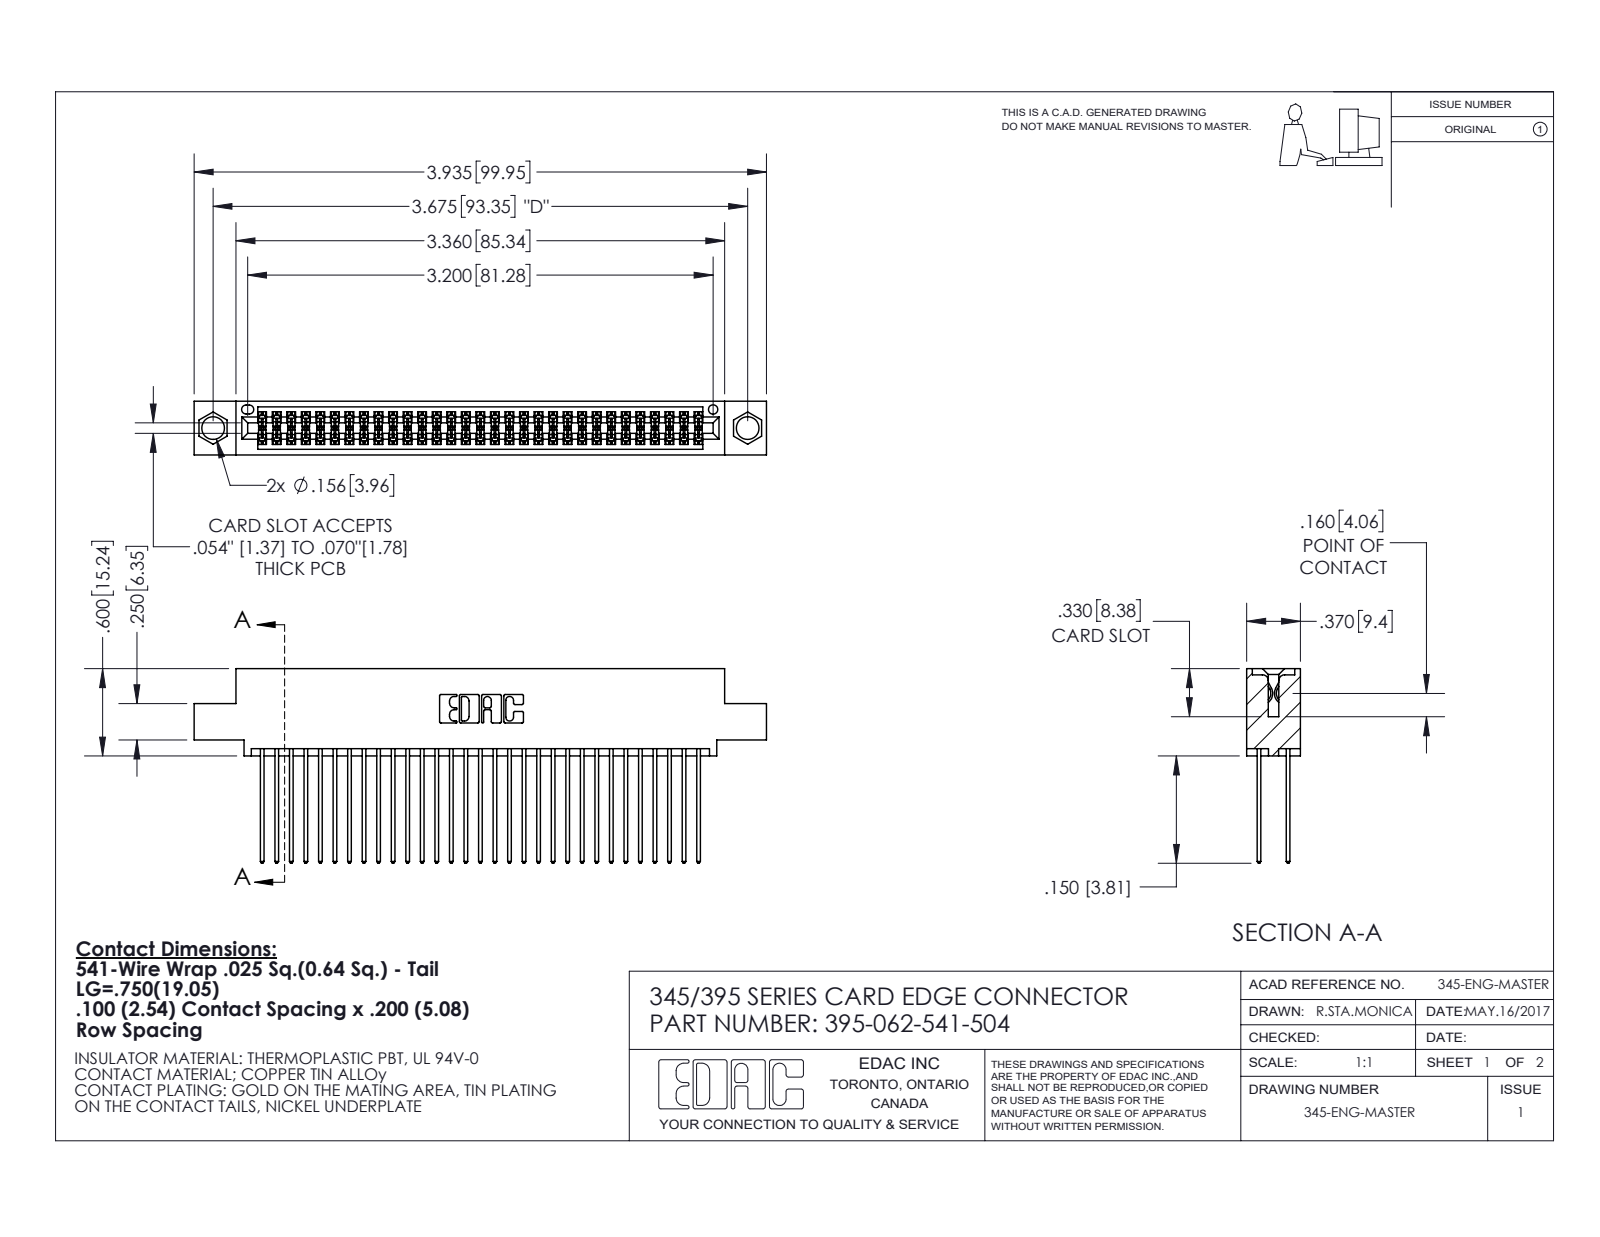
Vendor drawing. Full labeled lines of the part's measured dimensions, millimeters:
Part name (STEP PRODUCT): 345-292-001_345-293-141; 395-062-541-504; 345 Part_0.110 Offset - 0.156 Dia-TI
STEP written by: SolidWorks 2020 (CONFIG_CONTROL_DESIGN)
Units: millimetres
Bodies: 63 solids, 3244 faces (2144 planar, 1100 cylindrical, 0 other)
Overall size (bounding box): 99.9 × 34 × 9.4
Volume: 9 780 mm³ · Surface area: 15 860 mm²
Round holes (diameter × count): ⌀4 ×2, ⌀1.6 ×1
Partial cylindrical surfaces — rounded edges, fillets, slot ends (radius × count): R0.2 ×124, R0.3 ×62, R0.3 ×22, R0.2 ×6, R0.8 ×6, R0.7 ×3, R0.4 ×2, R0.5 ×2
Main face-to-face distances: 1.8, 7.6, 5.1, 2.5, 6.9, 0.6, 5.7, 9.4, 4.4, 3.8
Hole centre spacings: 6.9, 87.4, 93.3
